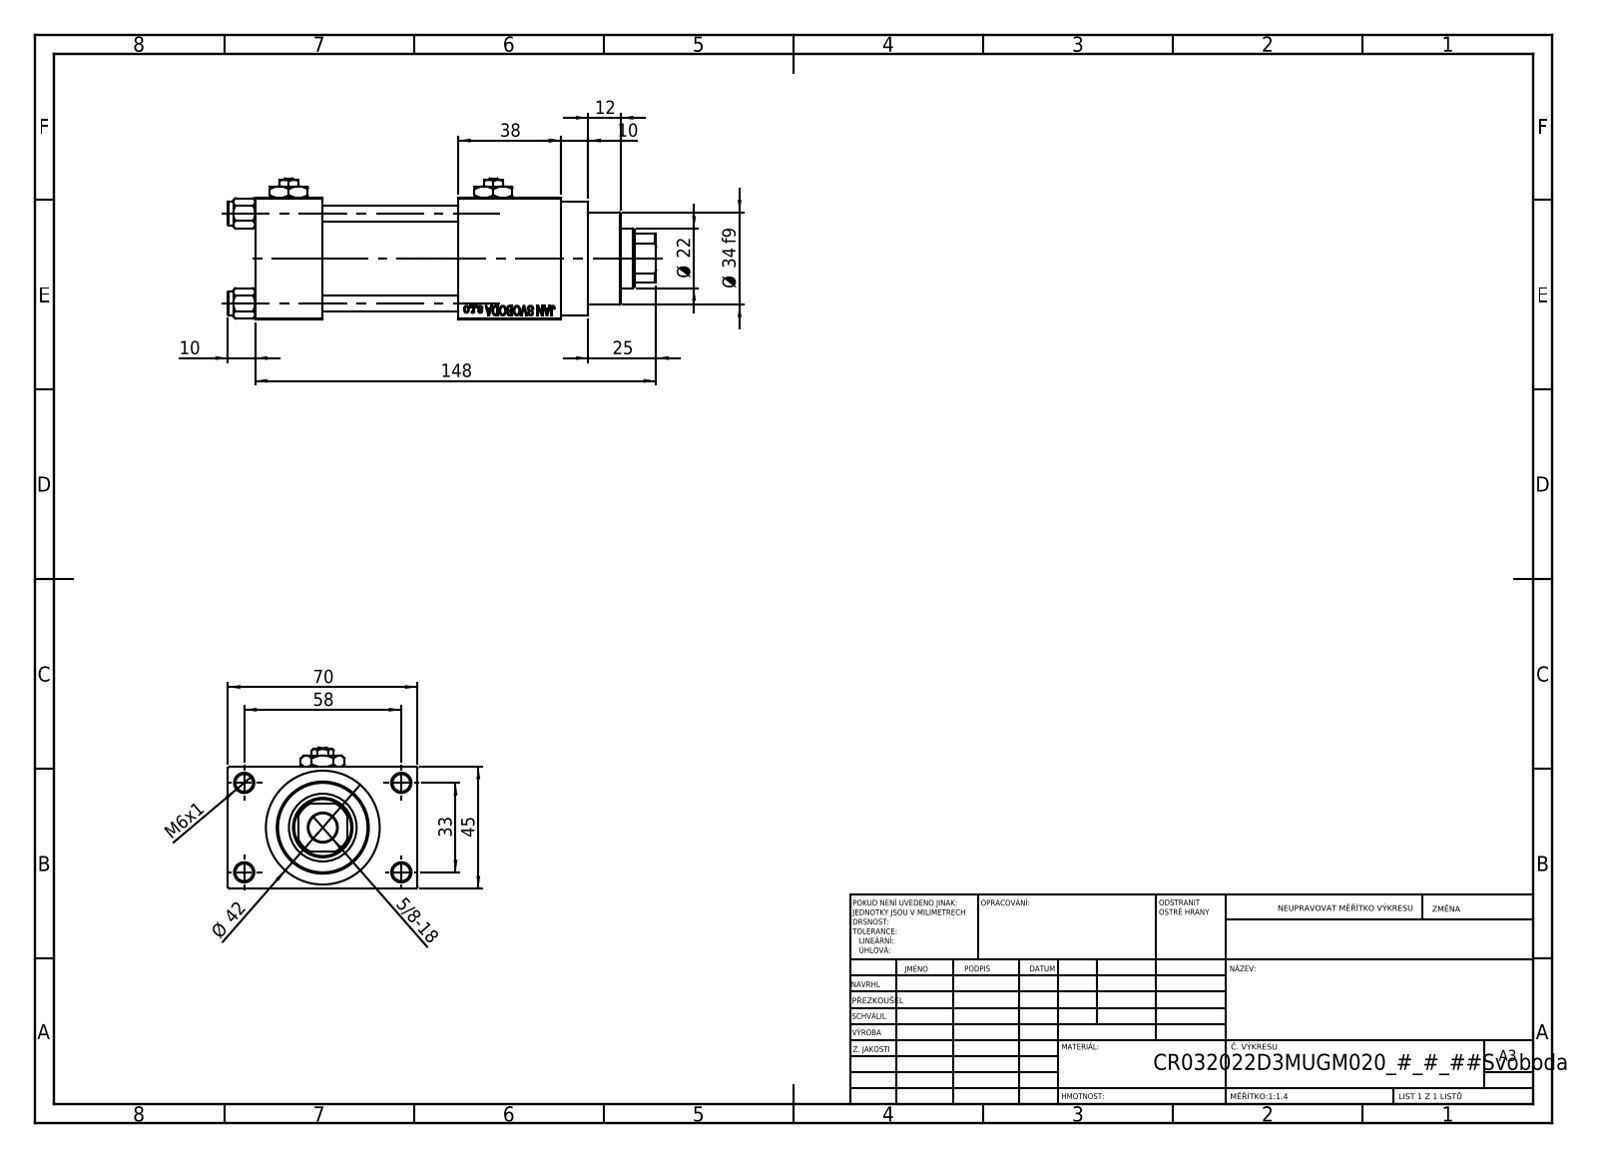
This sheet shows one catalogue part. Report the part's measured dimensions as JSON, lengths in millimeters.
{"part_name": "V215_VC_A; V215CR_D_Body; V215CR_D_TYCINKA; V215CR_VCP_D (+2 more)", "step_written_by": "SolidWorks 2019 (CONFIG_CONTROL_DESIGN)", "units": "millimeters", "bodies": {"solids": 13, "faces": 1201, "planar": 542, "cylindrical": 99, "other": 560}, "overall_size": [158, 70, 52], "volume_mm3": 243696, "surface_area_mm2": 81130, "round_holes": [[6, 4], [6.5, 4], [7, 3], [13.16, 3], [20, 3], [10.5, 1], [22, 1], [24, 1], [25, 1], [32, 1], [33, 1]], "round_bosses_or_shafts": [[9, 4], [42, 1], [38, 1], [34, 1]], "partial_cylinders_radius": [[10.5, 1]], "face_to_face_distances": [45, 25, 50, 75, 12.5, 57.5, 88, 70, 38, 113], "hole_center_spacings": [12.4, 23.48, 33.2, 33.37, 35.35, 45.6, 56.35, 33]}
